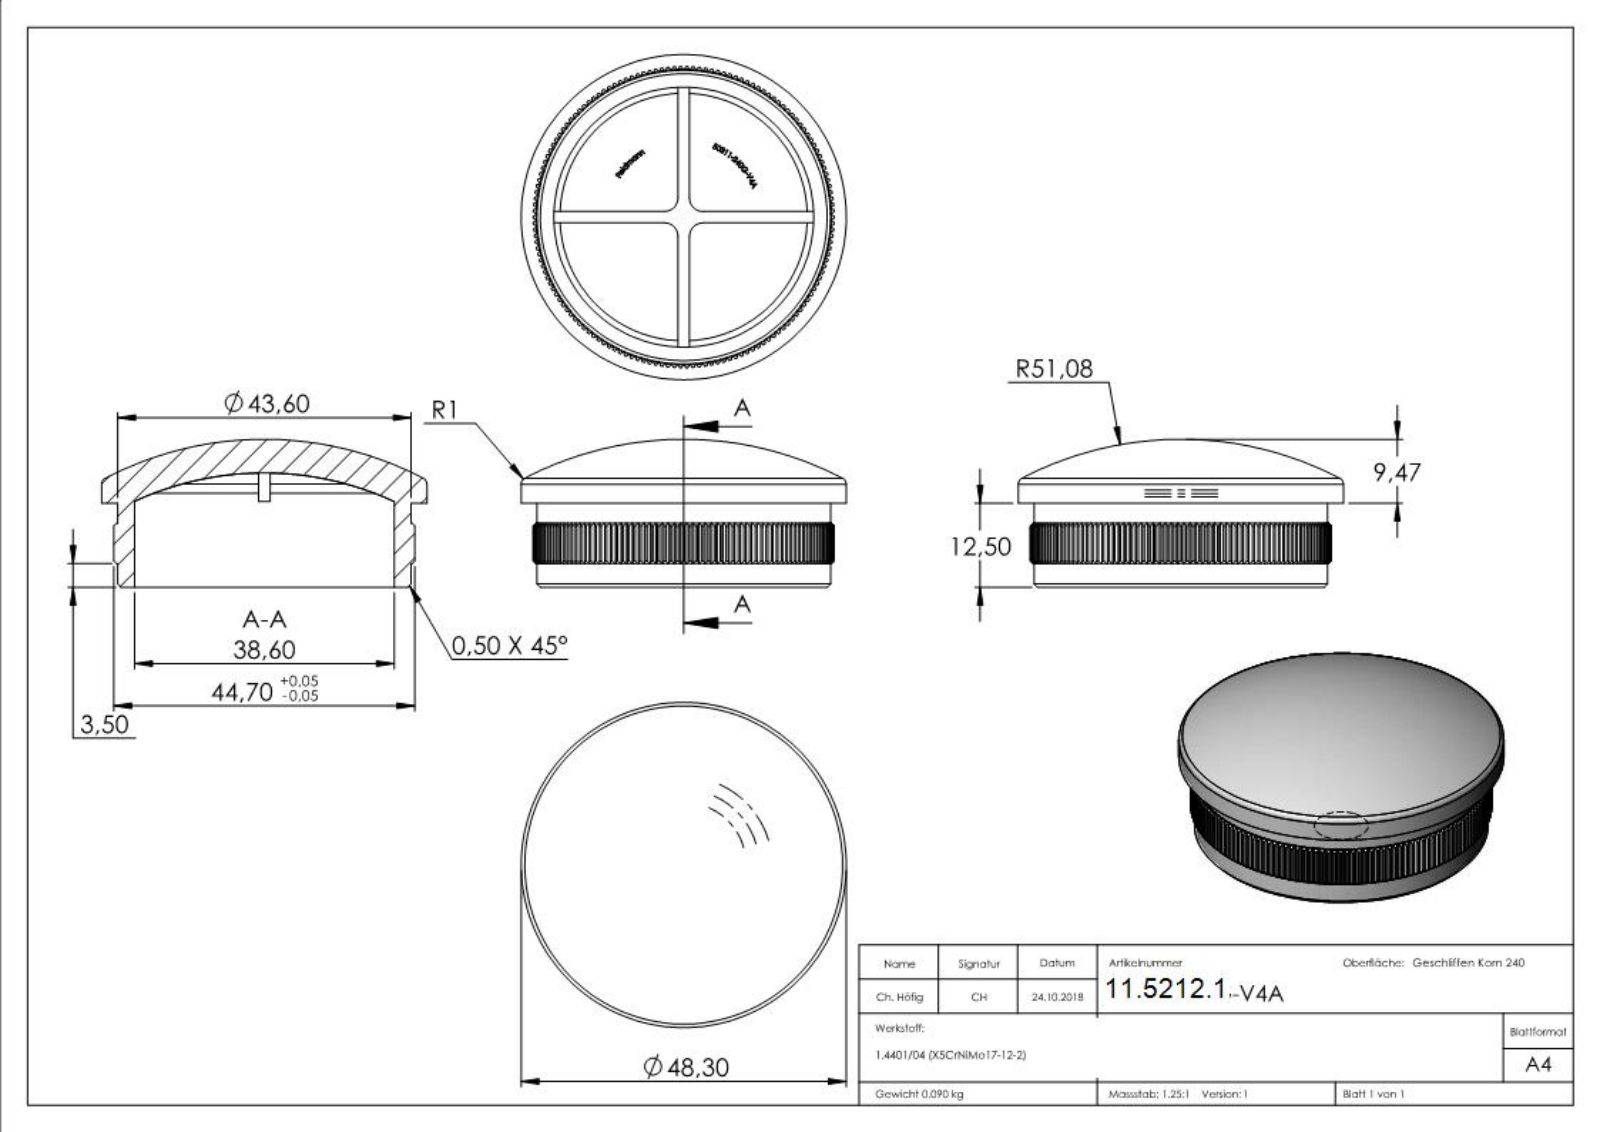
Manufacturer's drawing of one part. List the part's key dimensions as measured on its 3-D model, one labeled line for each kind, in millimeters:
Part name (STEP PRODUCT): 50311-240G-V4A
STEP written by: SolidWorks 2015 (CONFIG_CONTROL_DESIGN)
Units: millimetres
Bodies: 1 solid, 1358 faces (747 planar, 162 cylindrical, 449 other)
Overall size (bounding box): 48.3 × 48.3 × 21.97
Volume: 11 258 mm³ · Surface area: 8 697 mm²
Round holes (diameter × count): ⌀38.6 ×1
Round bosses / shafts (diameter × count): ⌀48.3 ×1, ⌀43.6 ×1
Partial cylindrical surfaces — rounded edges, fillets, slot ends (radius × count): R2 ×4, R22.35 ×1
Main face-to-face distances: 21.8, 12.5, 21.81, 1.7, 21.82, 21.79, 21.78, 9.5, 3, 3.5
